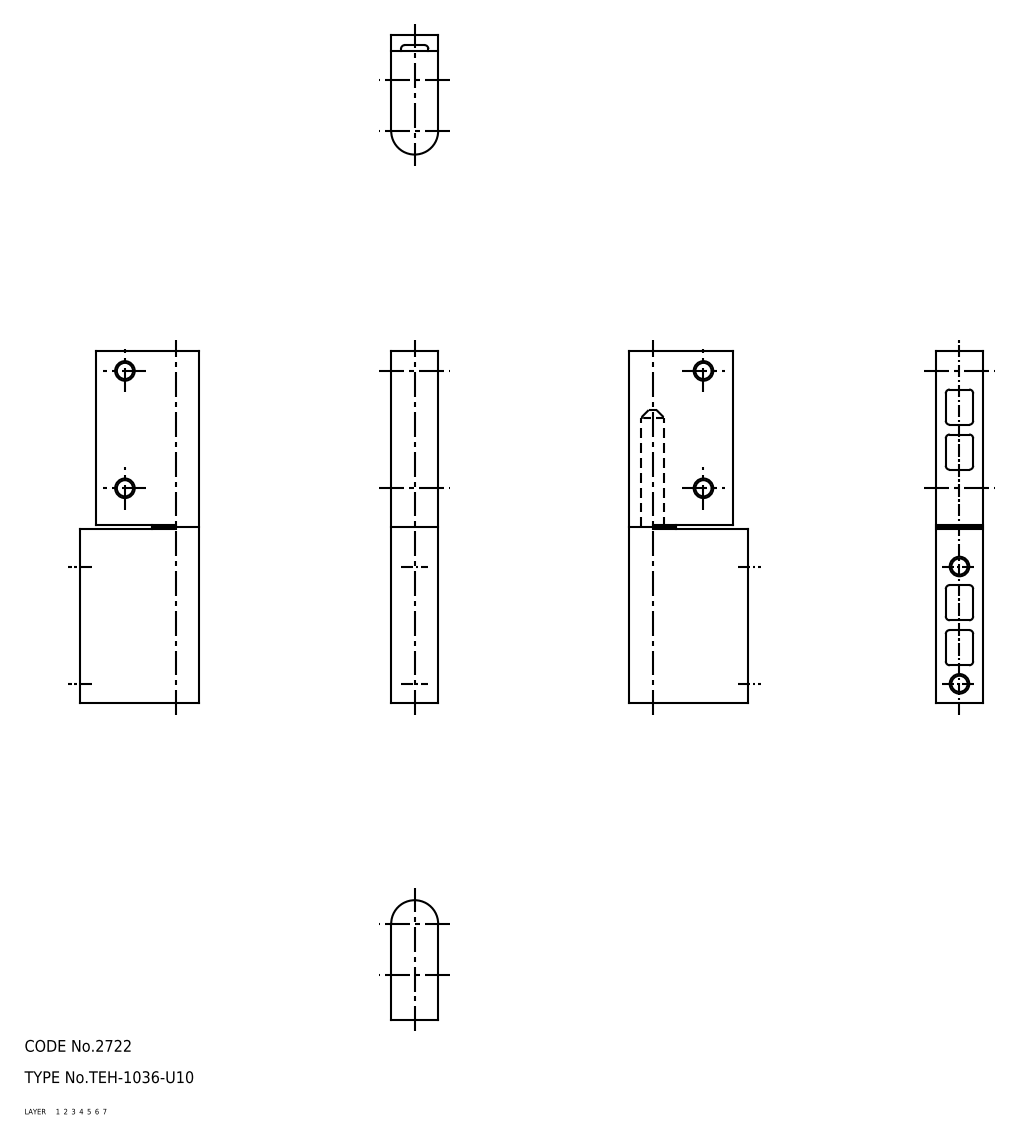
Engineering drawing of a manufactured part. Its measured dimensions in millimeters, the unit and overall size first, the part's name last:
Units: millimetres
Overall size (bounding box): 90 × 30.5 × 12
Volume: 23 062 mm³ · Surface area: 13 497 mm²
Bodies: 3 solids, 90 faces (0 planar, 0 cylindrical, 90 other)
Part name (STEP PRODUCT): shaft; hinge pieces_B; hinge pieces_A; TEH_1036_U10_2625_36
STEP written by: CADfix (AUTOMOTIVE_DESIGN)
